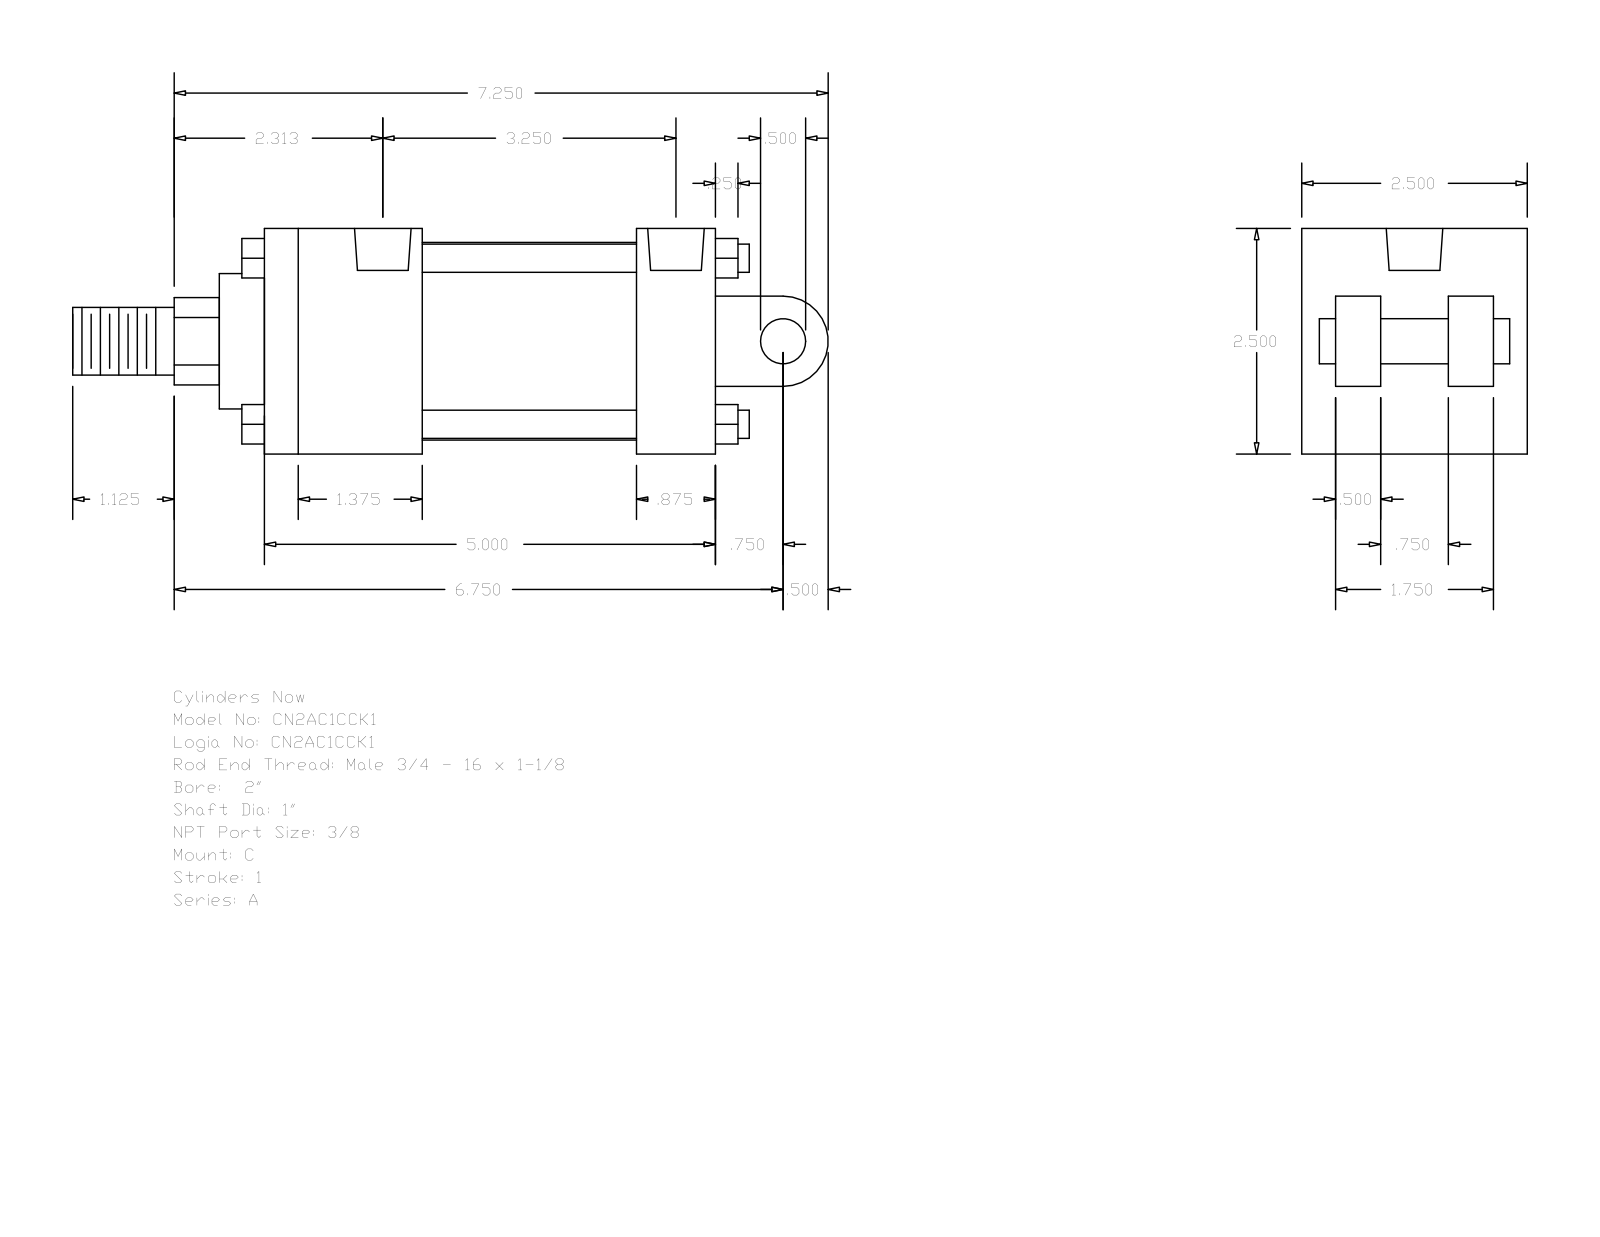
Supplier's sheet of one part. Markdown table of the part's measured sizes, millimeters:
| quantity | value |
| --- | --- |
| part name | A_C__0200_1 |
| STEP written by | GSSL Pune (CONFIG_CONTROL_DESIGN) |
| units | millimeters |
| bodies | 0 solids, 135 faces (102 planar, 33 cylindrical, 0 other) |
| overall size | 212.72 × 63.5 × 63.5 |
| round holes (diameter × count) | 5.56 × 4, 15.93 × 2 |
| round bosses / shafts (diameter × count) | 7.94 × 4, 55.63 × 1, 38.1 × 1, 25.4 × 1, 19.05 × 1, 12.7 × 1 |
| partial cylindrical surfaces (radius × count) | 12.29 × 1, 12.7 × 1 |
| main face-to-face distances | 63.5, 22.22, 127, 44.45, 12.7, 82.55, 104.78, 60.33, 9.52, 41.28 |
| hole center spacings | 76.98, 1.59, 3.98, 78.57, 80.96, 82.55 |
